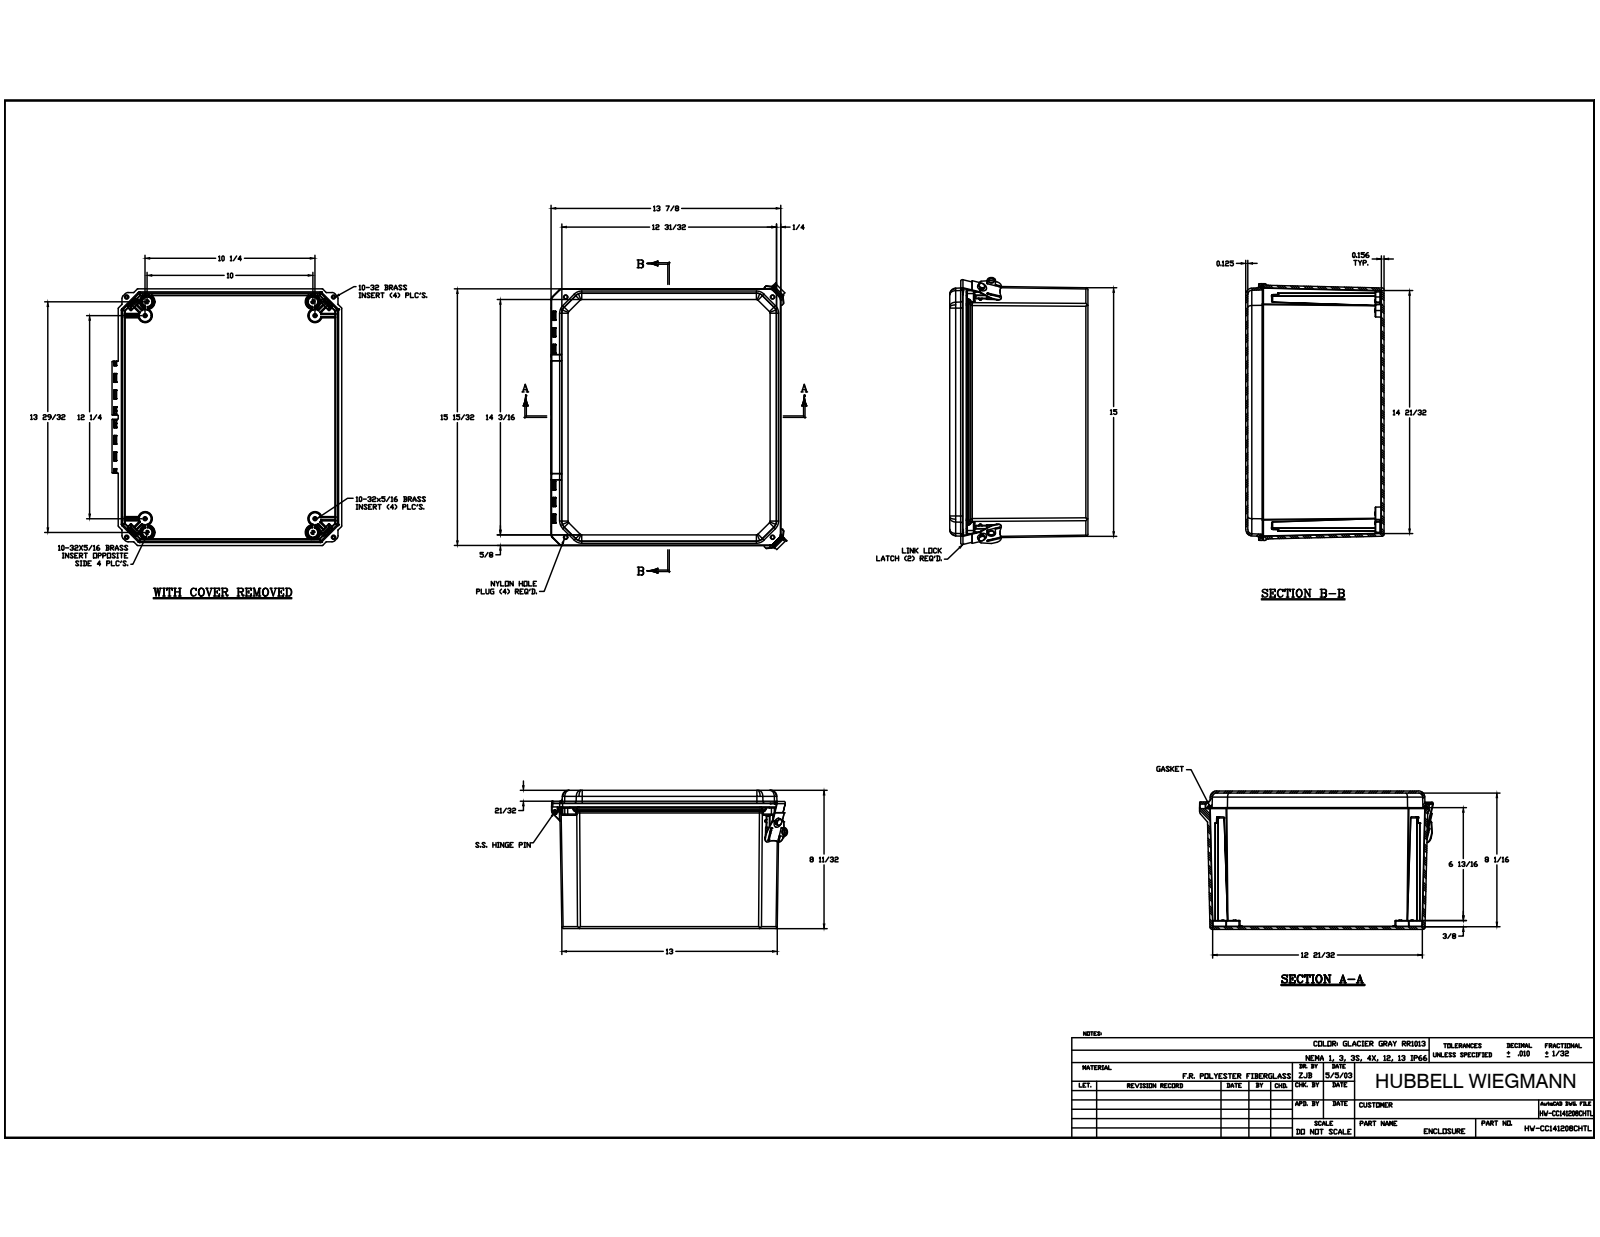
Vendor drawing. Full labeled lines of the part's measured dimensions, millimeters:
Part name (STEP PRODUCT): DS141208BOX; DSCC141206CVR; GA141206; WP1412HLU (+5 more)
STEP written by: Autodesk Inventor 2014 (AUTOMOTIVE_DESIGN)
Units: millimetres
Bodies: 31 solids, 2388 faces (713 planar, 936 cylindrical, 739 other)
Overall size (bounding box): 417.01 × 363.97 × 211.91
Volume: 2 220 000 mm³ · Surface area: 1 172 000 mm²
Round holes (diameter × count): ⌀3.96 ×12, ⌀3.86 ×8, ⌀2.49 ×4, ⌀3.81 ×4, ⌀5.56 ×4, ⌀6.4 ×4, ⌀7.92 ×4, ⌀1.27 ×2, ⌀3.05 ×2, ⌀9.22 ×2, ⌀3.48 ×1
Round bosses / shafts (diameter × count): ⌀6.25 ×12, ⌀5.3 ×4, ⌀5.08 ×4, ⌀3.43 ×3, ⌀15.24 ×2, ⌀1.27 ×2
Partial cylindrical surfaces — rounded edges, fillets, slot ends (radius × count): R0.25 ×222, R0.13 ×116, R0.51 ×59, R3.17 ×41, R0.76 ×38, R0.99 ×28, R6.35 ×26, R0.76 ×24
Main face-to-face distances: 3.17, 3.96, 211.91, 207.95, 208.74, 204.78, 4.07, 4.03, 186.51, 25.4
Hole centre spacings: 40.23, 445.78, 459.83, 10.9, 20.15, 21.02, 32.54, 258.01
